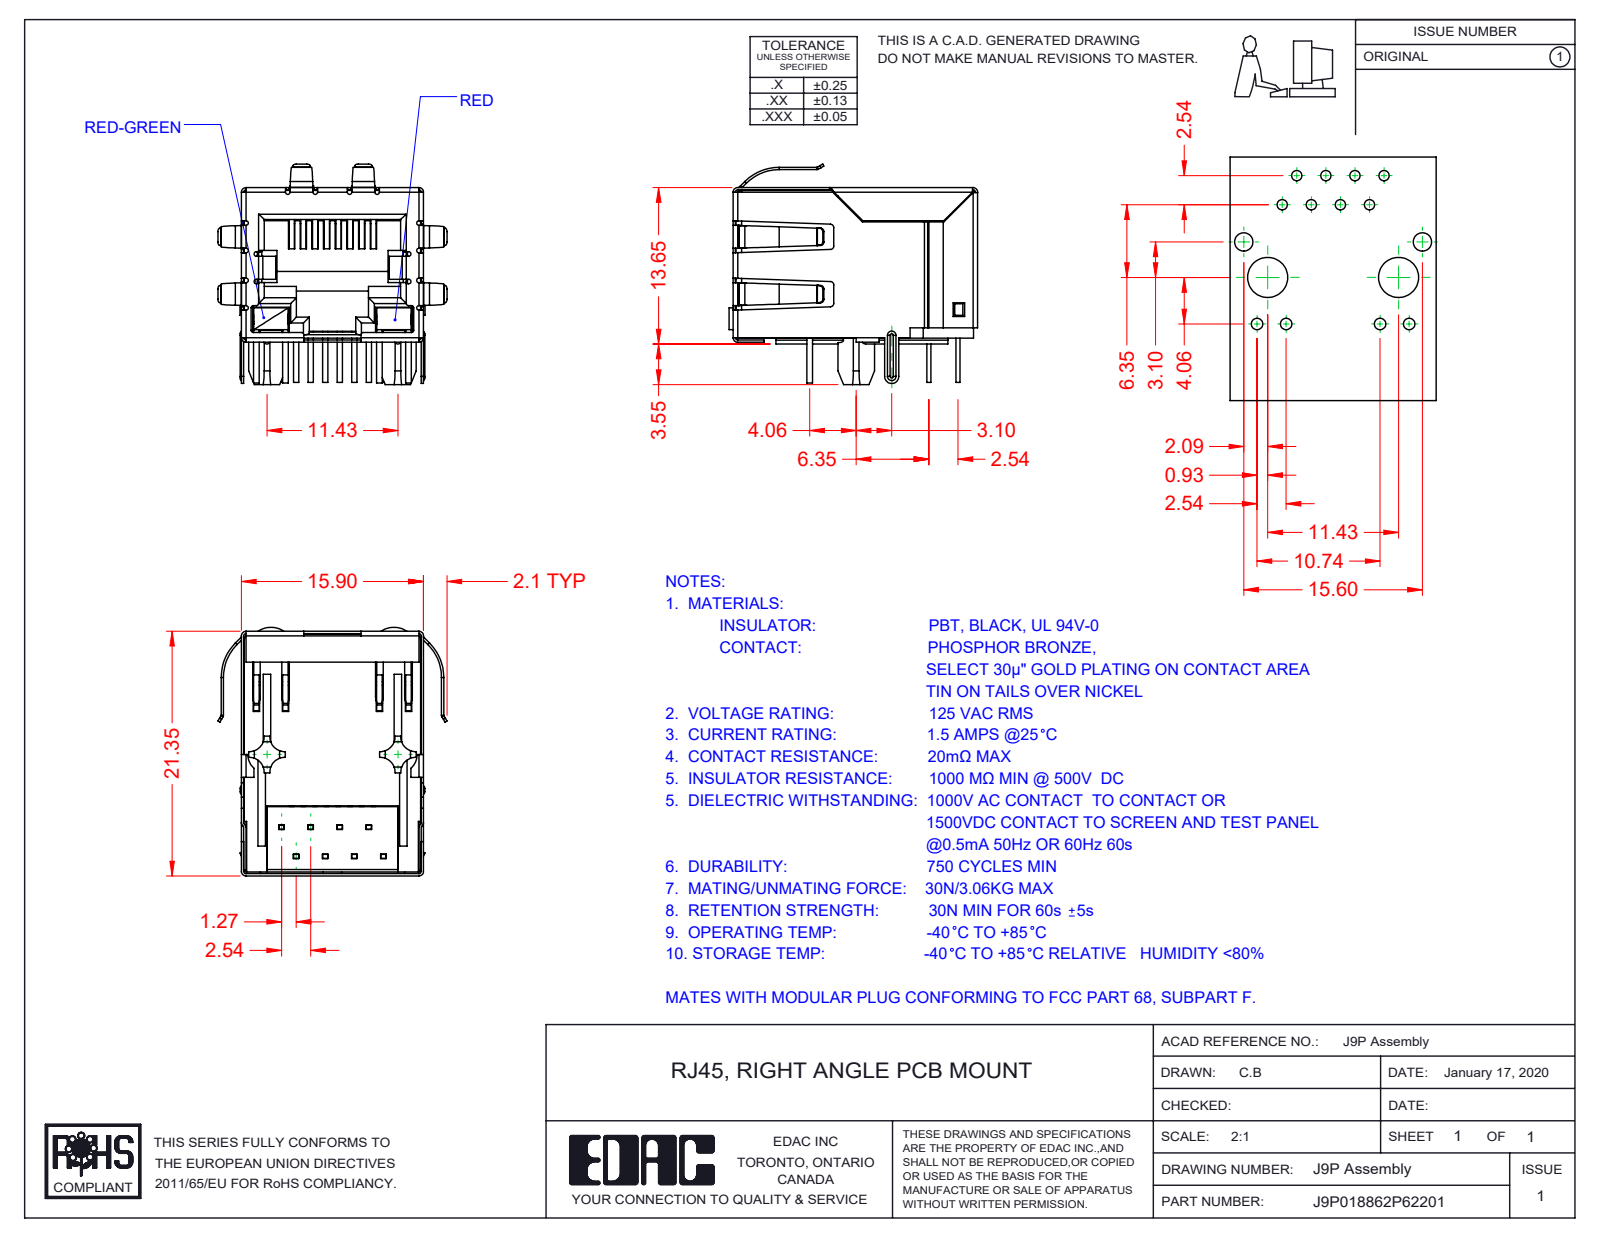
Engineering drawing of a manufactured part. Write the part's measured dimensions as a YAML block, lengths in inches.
part_name: "9P-LED LED LH_6-Red-Green; 9P-LED Insulator; J9P018862P62202; 9P-LED LED RH_2-Red (+4 more)"
step_written_by: "SolidWorks 2016 (CONFIG_CONTROL_DESIGN)"
units: inches
bodies: {solids: 13, faces: 1474, planar: 1042, cylindrical: 338, other: 94}
overall_size: [0.854, 0.787, 0.758]
volume: 0.164
surface_area: 11.65
partial_cylinders:
  - {radius: 0.008, count: 39}
  - {radius: 0.02, count: 22}
  - {radius: 0.012, count: 20}
  - {radius: 0.016, count: 16}
  - {radius: 0.051, count: 8}
  - {radius: 0.009, count: 5}
  - {radius: 0.004, count: 4}
  - {radius: 0.012, count: 4}
face_to_face_distances: [0.608, 0.618, 0.616, 0.014, 0.021, 0.61, 0.487, 0.024, 0.055, 0.023]
